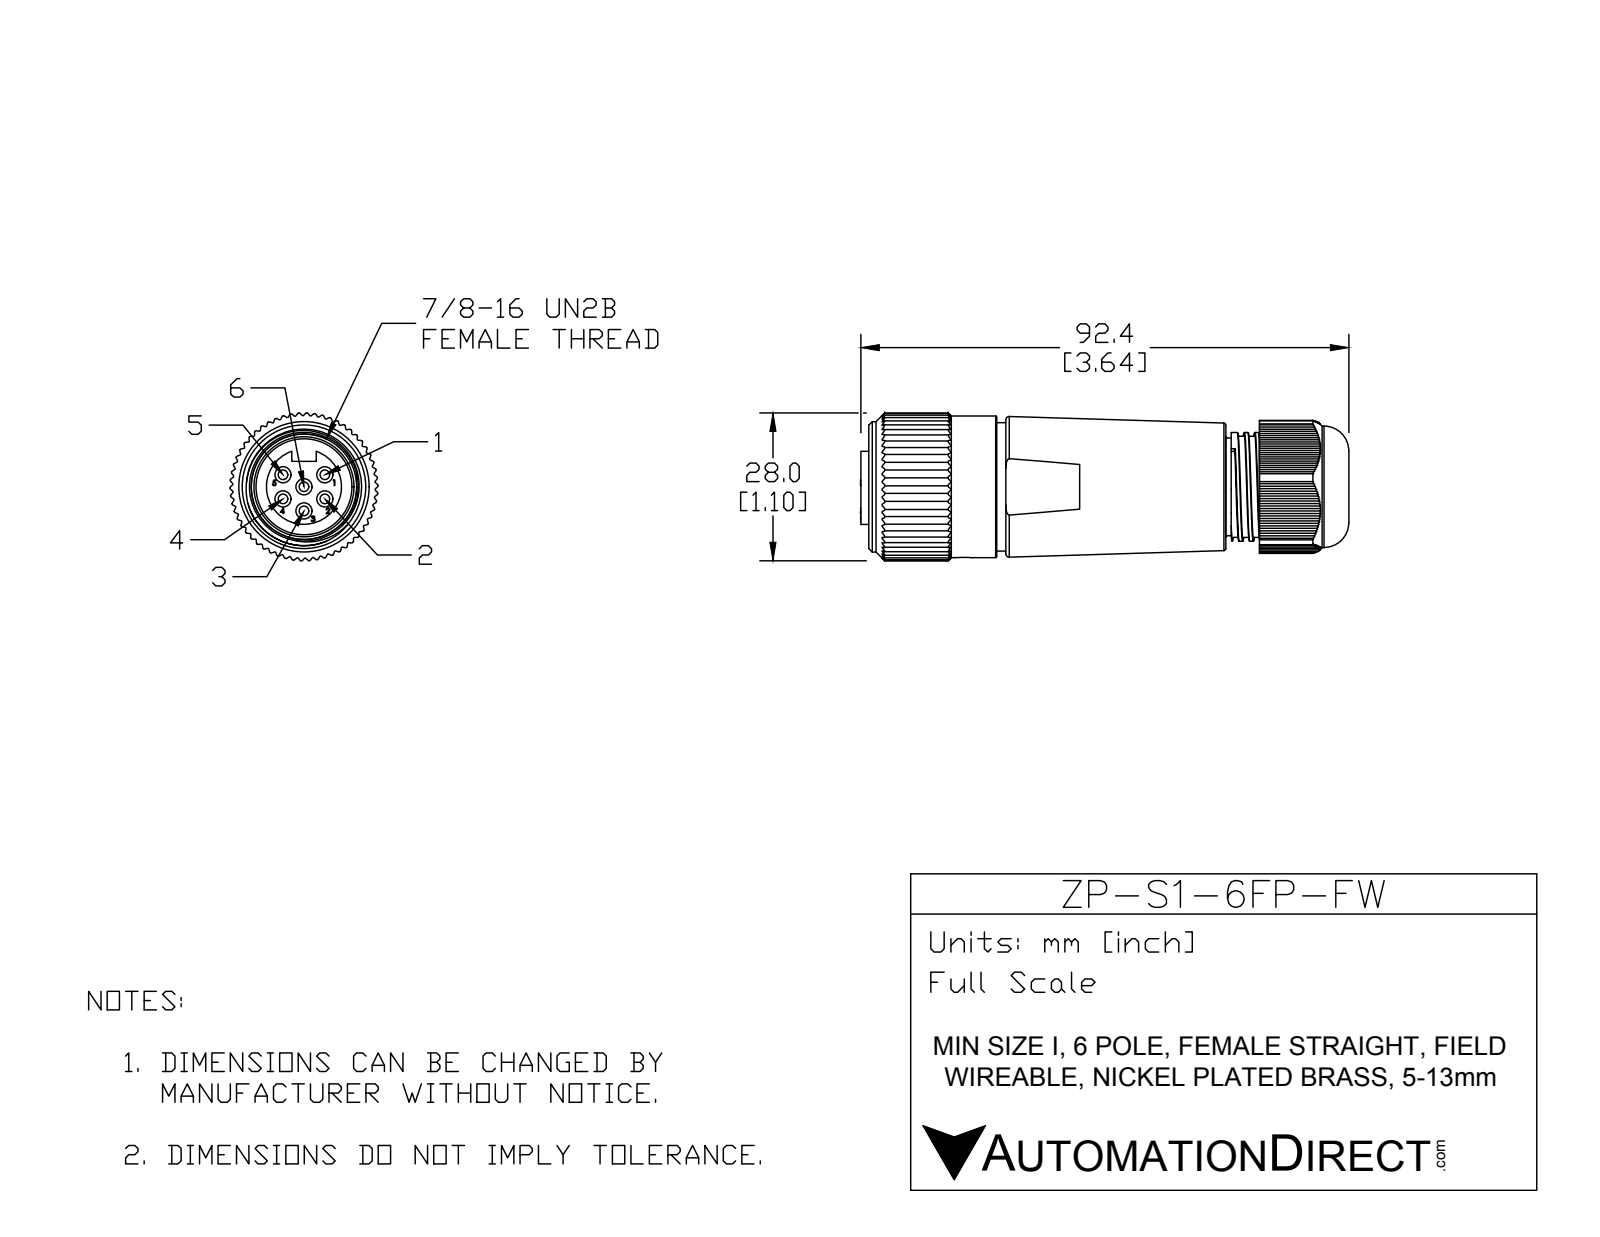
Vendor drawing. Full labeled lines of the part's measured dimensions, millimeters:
Part name (STEP PRODUCT): ZP-S1-6FP-FW
STEP written by: SolidWorks 2015 (AUTOMOTIVE_DESIGN)
Units: millimetres
Bodies: 4 solids, 827 faces (462 planar, 306 cylindrical, 59 other)
Overall size (bounding box): 93.57 × 27.99 × 27.98
Volume: 41 969 mm³ · Surface area: 14 513 mm²
Round holes (diameter × count): ⌀3.05 ×6, ⌀3.56 ×1, ⌀13.46 ×1, ⌀20.58 ×1, ⌀21.57 ×1, ⌀24.2 ×1, ⌀25.4 ×1
Round bosses / shafts (diameter × count): ⌀26.8 ×1, ⌀24.68 ×1, ⌀24.3 ×1, ⌀22.99 ×1, ⌀20.6 ×1, ⌀18.14 ×1, ⌀14.22 ×1
Partial cylindrical surfaces — rounded edges, fillets, slot ends (radius × count): R0.25 ×165, R13.23 ×1, R14 ×1
Main face-to-face distances: 69.12, 1.06, 0.35, 0.71, 8.79, 60.33, 1.41, 2.12, 1.77, 0.5
Hole centre spacings: 4.57, 4.56, 7.91, 7.92, 9.14
